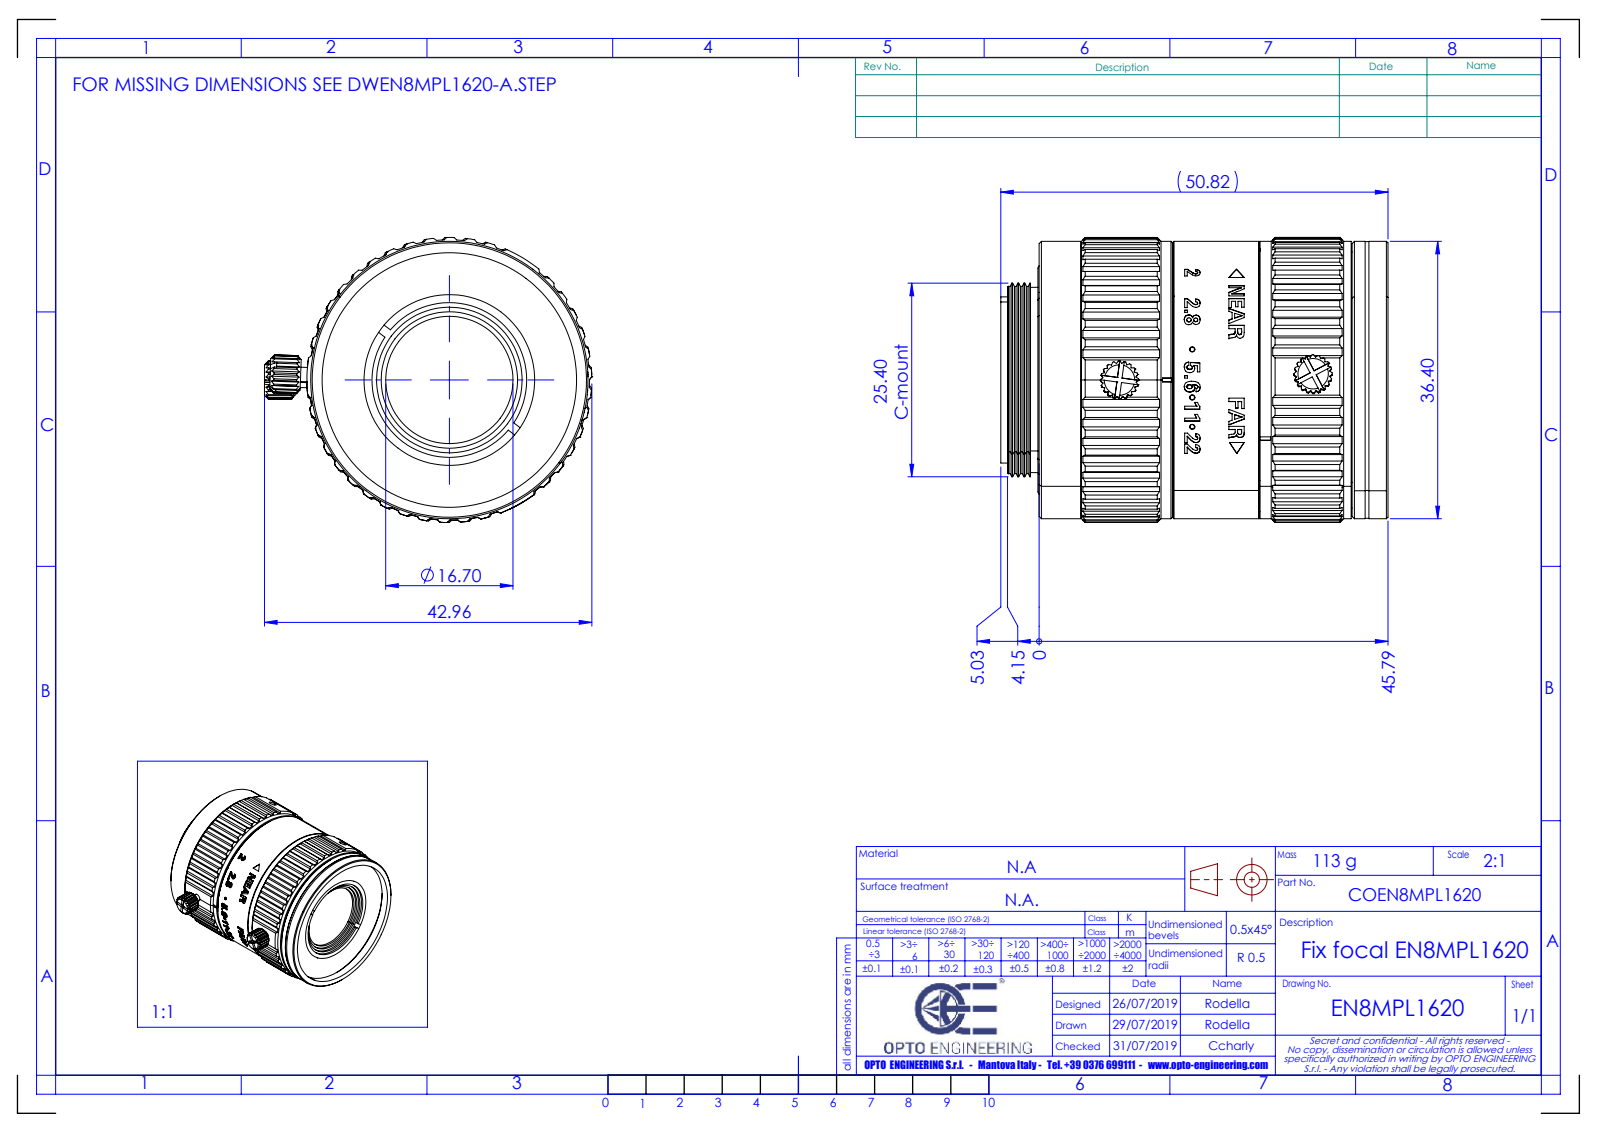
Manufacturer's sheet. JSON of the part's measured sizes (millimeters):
{"part_name": "EN8MPL1620-02; EN8MPL1620-03; EN8MPL1620-04; EN8MPL1620-06 (+8 more)", "step_written_by": "PRO/ENGINEER BY PARAMETRIC TECHNOLOGY CORPORATION, 2015240 (CONFIG_CONTROL_DESIGN)", "units": "millimeters", "bodies": {"solids": 23, "faces": 1681, "planar": 697, "cylindrical": 362, "other": 622}, "overall_size": [50.82, 39.28, 37.4], "volume_mm3": 9541, "surface_area_mm2": 20654, "round_holes": [[2, 6], [3, 4], [0.33, 2], [2.6, 1], [16.7, 1], [17.4, 1], [17.9, 1], [18.6, 1], [18.9, 1], [19.1, 1], [19.9, 1], [20.3, 1]], "round_bosses_or_shafts": [[2.8, 4], [2, 2], [36.4, 1], [36.3, 1], [35.2, 1], [33.6, 1], [25.4, 1], [24.54, 1]], "partial_cylinders_radius": [[1.5, 8], [0.6, 3], [0.65, 3], [1.05, 3], [1, 2], [2.21, 2], [2.5, 2], [0.56, 1]], "face_to_face_distances": [42.84, 45.73, 2.89, 0.6, 2.44, 43.29, 0.45, 40.64, 2.2, 43.44], "hole_center_spacings": [15.05, 21.28, 30.1, 0.31, 1.01, 14.74, 15.04, 15.07]}
